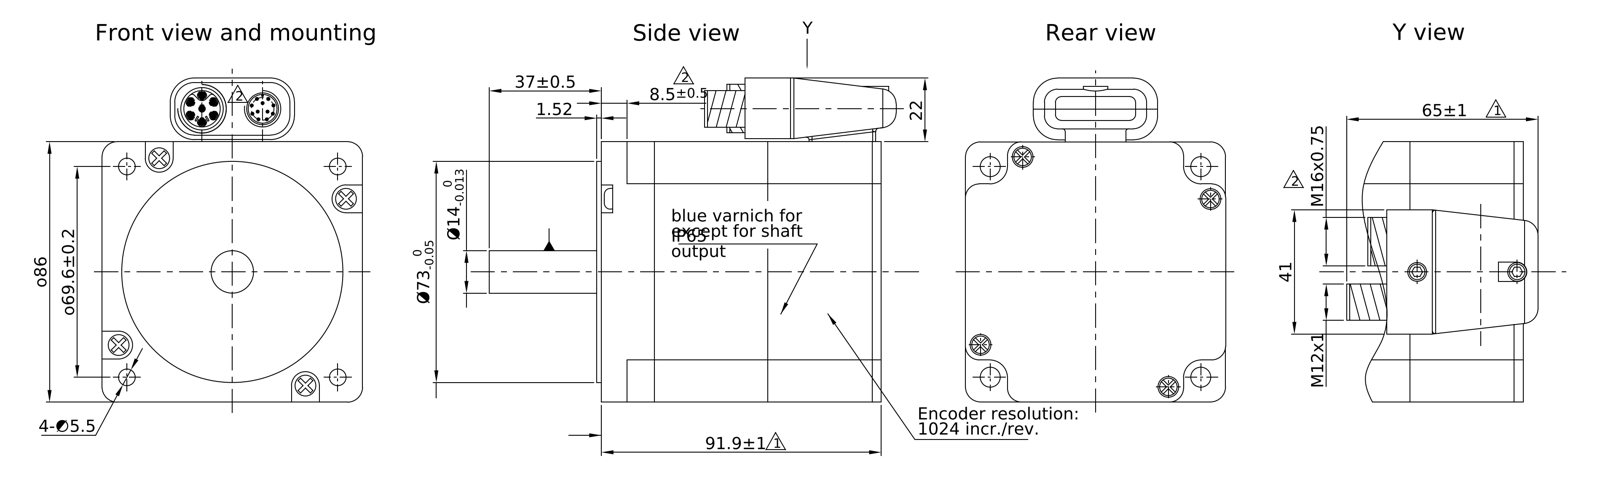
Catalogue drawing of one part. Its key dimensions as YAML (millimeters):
part_name: "零件1"
step_written_by: "Autodesk Inventor 2013 (AUTOMOTIVE_DESIGN)"
units: millimeters
bodies: {solids: 0, faces: 621, planar: 252, cylindrical: 183, other: 186}
overall_size: [132.9, 108.11, 85.9]
round_holes:
  - {diameter: 4, count: 5}
  - {diameter: 3, count: 4}
  - {diameter: 3.4, count: 4}
  - {diameter: 5.5, count: 4}
  - {diameter: 8.5, count: 1}
  - {diameter: 12, count: 1}
  - {diameter: 13, count: 1}
  - {diameter: 15, count: 1}
  - {diameter: 17, count: 1}
  - {diameter: 22.5, count: 1}
  - {diameter: 32, count: 1}
  - {diameter: 79.5, count: 1}
round_bosses_or_shafts:
  - {diameter: 0.8, count: 12}
  - {diameter: 3, count: 9}
  - {diameter: 1.25, count: 7}
  - {diameter: 5.5, count: 4}
  - {diameter: 2.73, count: 4}
  - {diameter: 2.69, count: 4}
  - {diameter: 5.54, count: 2}
  - {diameter: 73, count: 1}
partial_cylinders:
  - {radius: 4.6, count: 25}
  - {radius: 2, count: 12}
  - {radius: 5.9, count: 9}
  - {radius: 3, count: 7}
  - {radius: 4, count: 7}
  - {radius: 2.6, count: 4}
  - {radius: 5.5, count: 4}
  - {radius: 6, count: 4}
face_to_face_distances: [35.5, 34.4, 69.9, 3, 2, 37.4, 72.9, 18, 21, 16.4]
hole_center_spacings: [49.21, 11.14, 59.22, 64.41, 44.93, 45.54, 63.54, 69.6]
